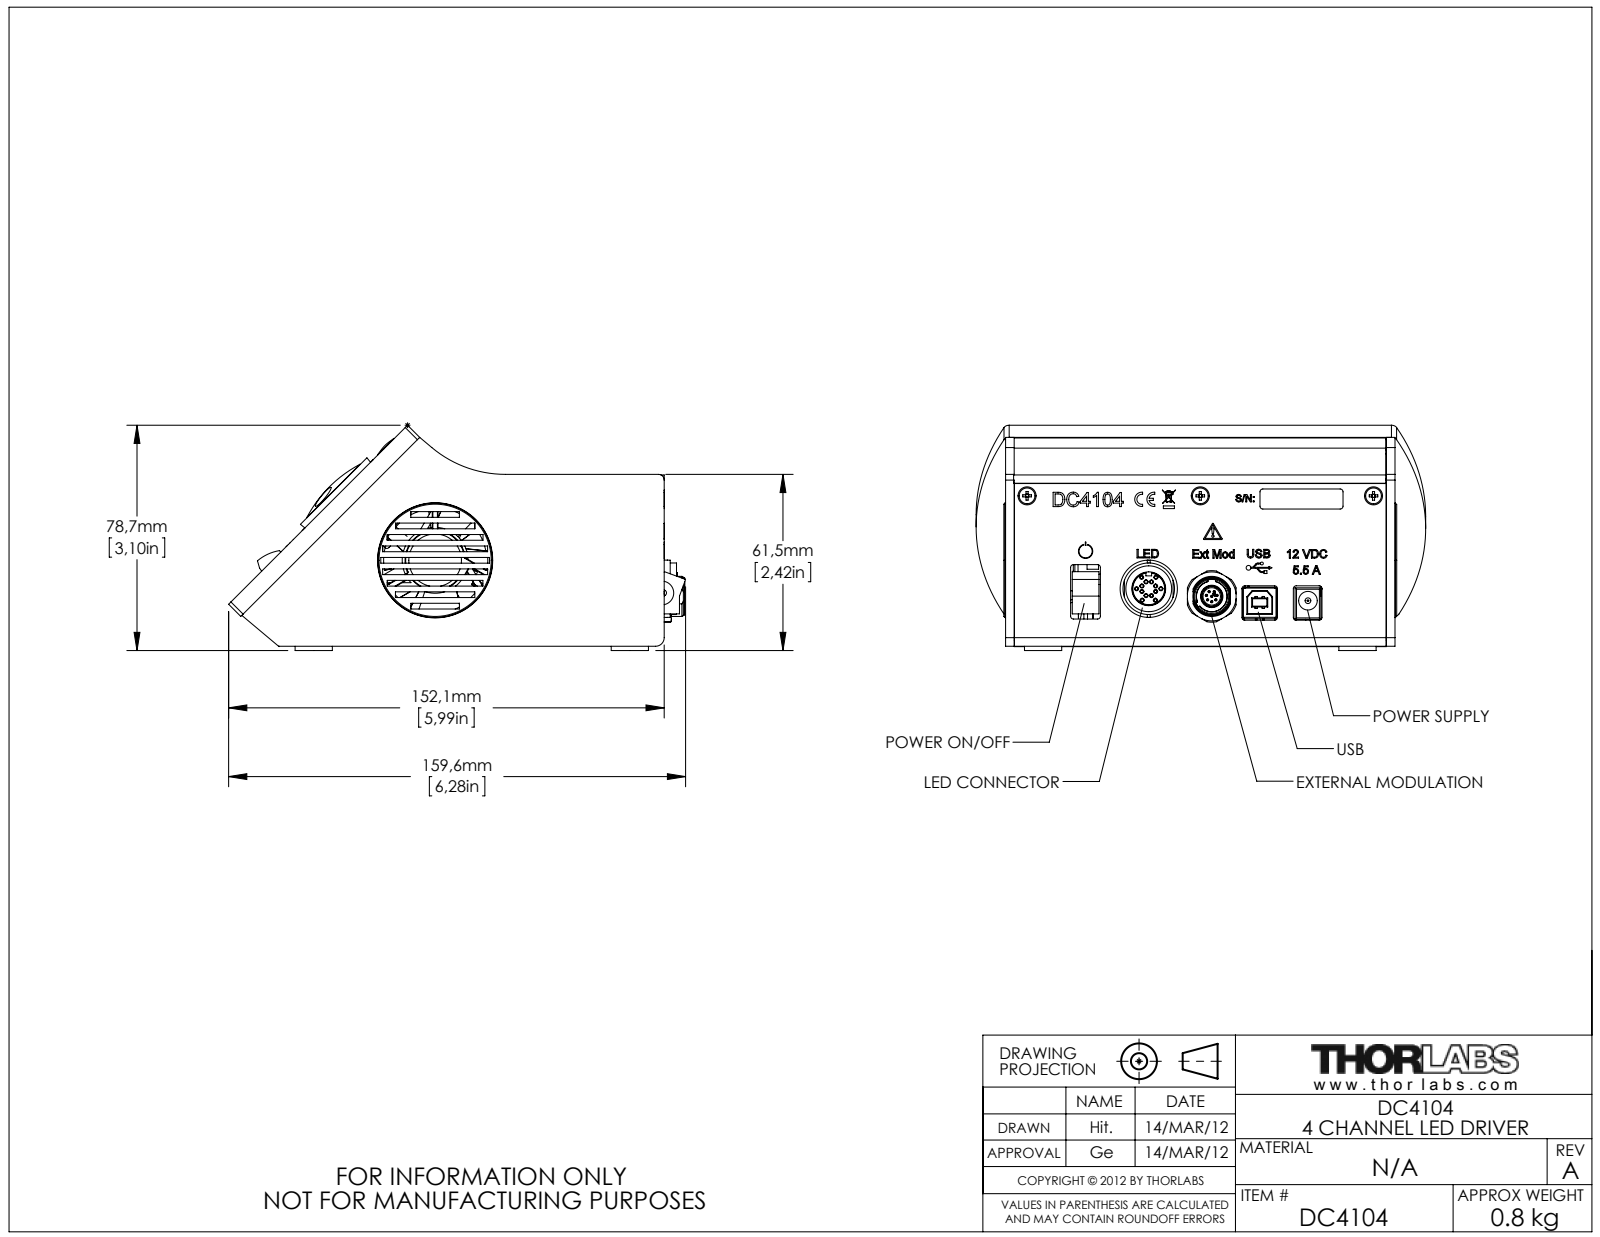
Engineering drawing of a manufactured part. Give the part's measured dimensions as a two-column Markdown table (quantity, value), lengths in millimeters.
| quantity | value |
| --- | --- |
| part name | 21569-E0W |
| STEP written by | SolidWorks 2011 (CONFIG_CONTROL_DESIGN) |
| units | millimeters |
| bodies | 0 solids, 776 faces (450 planar, 202 cylindrical, 124 other) |
| overall size | 159.59 × 157.01 × 78.65 |
| round holes (diameter × count) | 1 × 13, 8.5 × 1, 10.7 × 1, 12.3 × 1, 12.4 × 1, 16 × 1, 40.2 × 1 |
| round bosses / shafts (diameter × count) | 5.5 × 7, 13 × 4, 40 × 1, 26.27 × 1, 20 × 1, 12.9 × 1, 11.5 × 1, 6.5 × 1 |
| partial cylindrical surfaces (radius × count) | 1 × 28, 3 × 8, 0.5 × 7, 0.2 × 6, 2 × 5, 0.3 × 3, 0.15 × 2, 1.75 × 2 |
| main face-to-face distances | 3, 56.8, 133, 53.8, 6, 59.8, 136, 2, 130, 4 |
| hole center spacings | 2.58, 3.65, 1.9, 2.05, 3.05, 4.74, 4.8, 4.95 |
